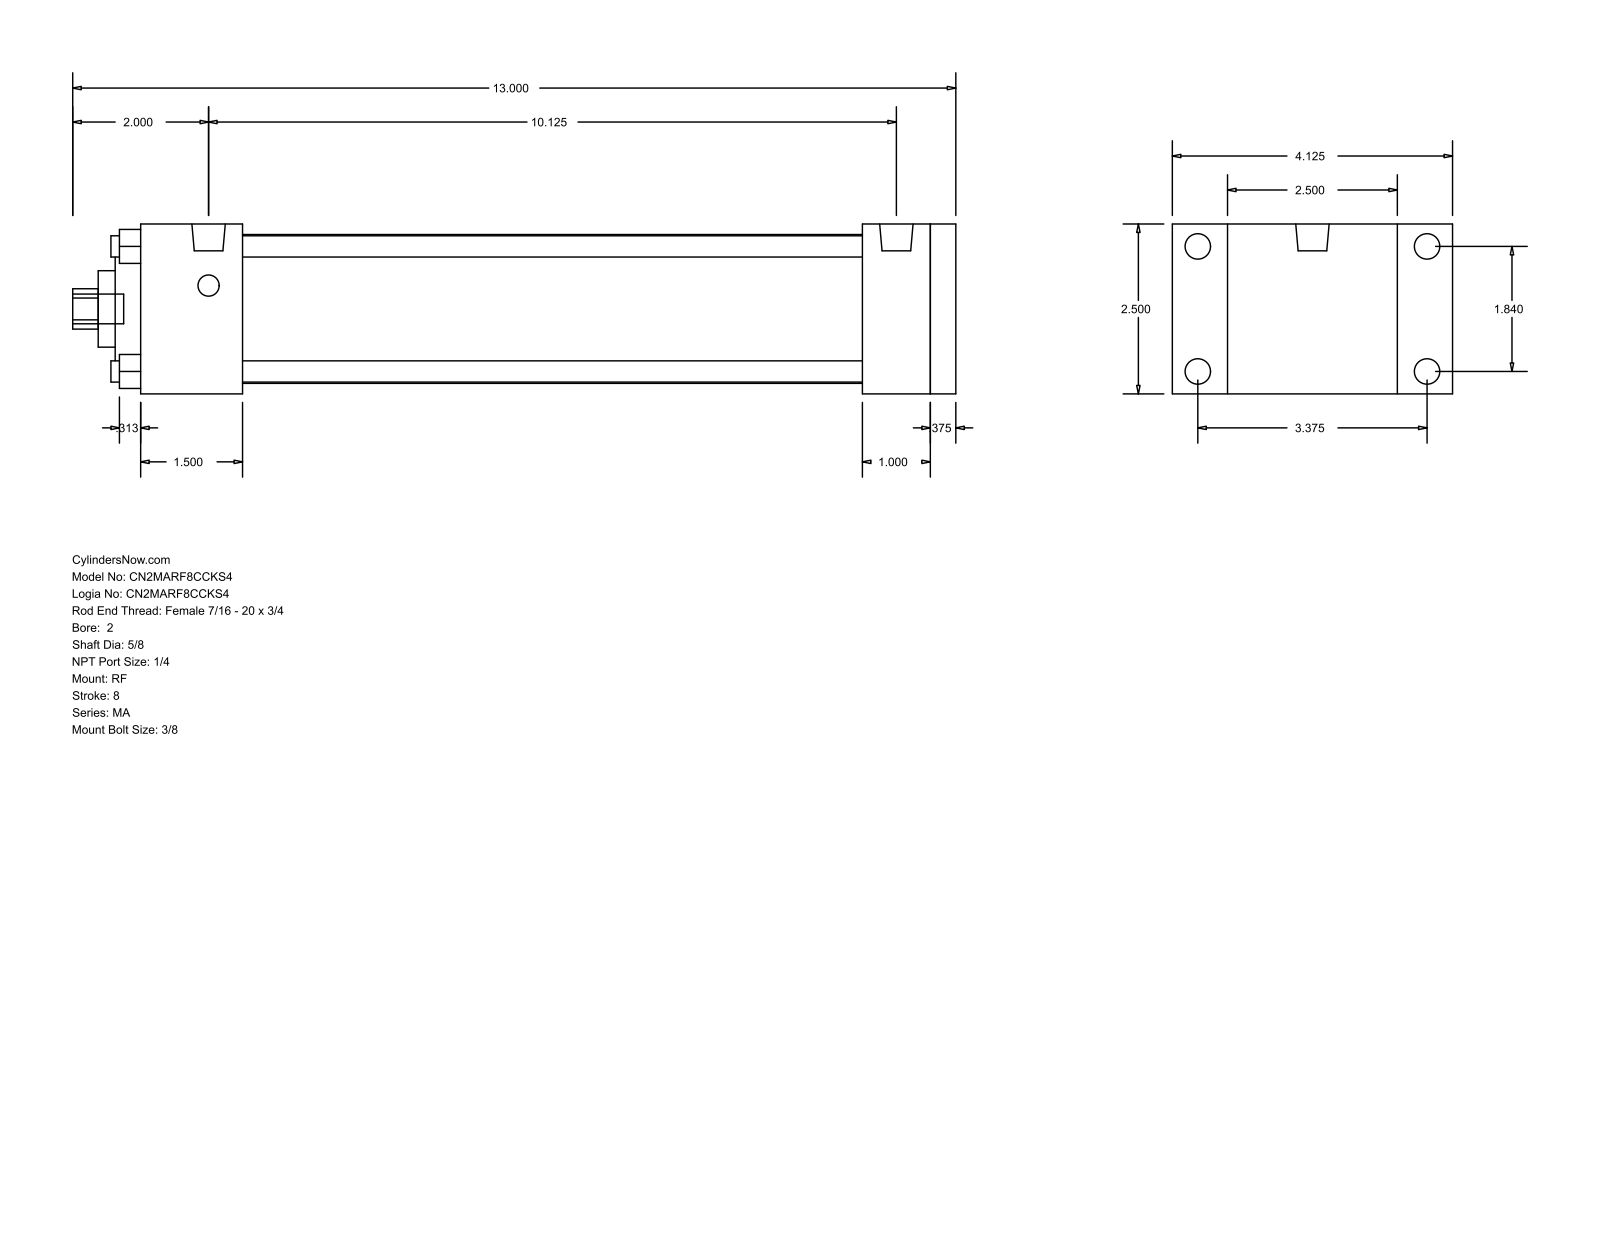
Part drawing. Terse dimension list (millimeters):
name: MA_RF__0200_0.625
written by: GSSL Pune (CONFIG_CONTROL_DESIGN)
unit: mm
bodies: 0 solids, 94 faces (65 planar, 29 cylindrical, 0 other)
size: 330.2 × 104.78 × 63.5
holes: 4× ⌀7.94, 1× ⌀15.88, 1× ⌀28.57, 1× ⌀50.8, 1× ⌀55.63
bosses: 4× ⌀9.53, 4× ⌀7.94, 2× ⌀12.49, 1× ⌀11.11
rounds: 1× R7.54
face distances: 63.5, 9.52, 304.8, 38.1, 295.28, 257.18, 266.7, 269.87, 231.77, 25.41
hole spacings: 33.05, 46.74, 66.1
